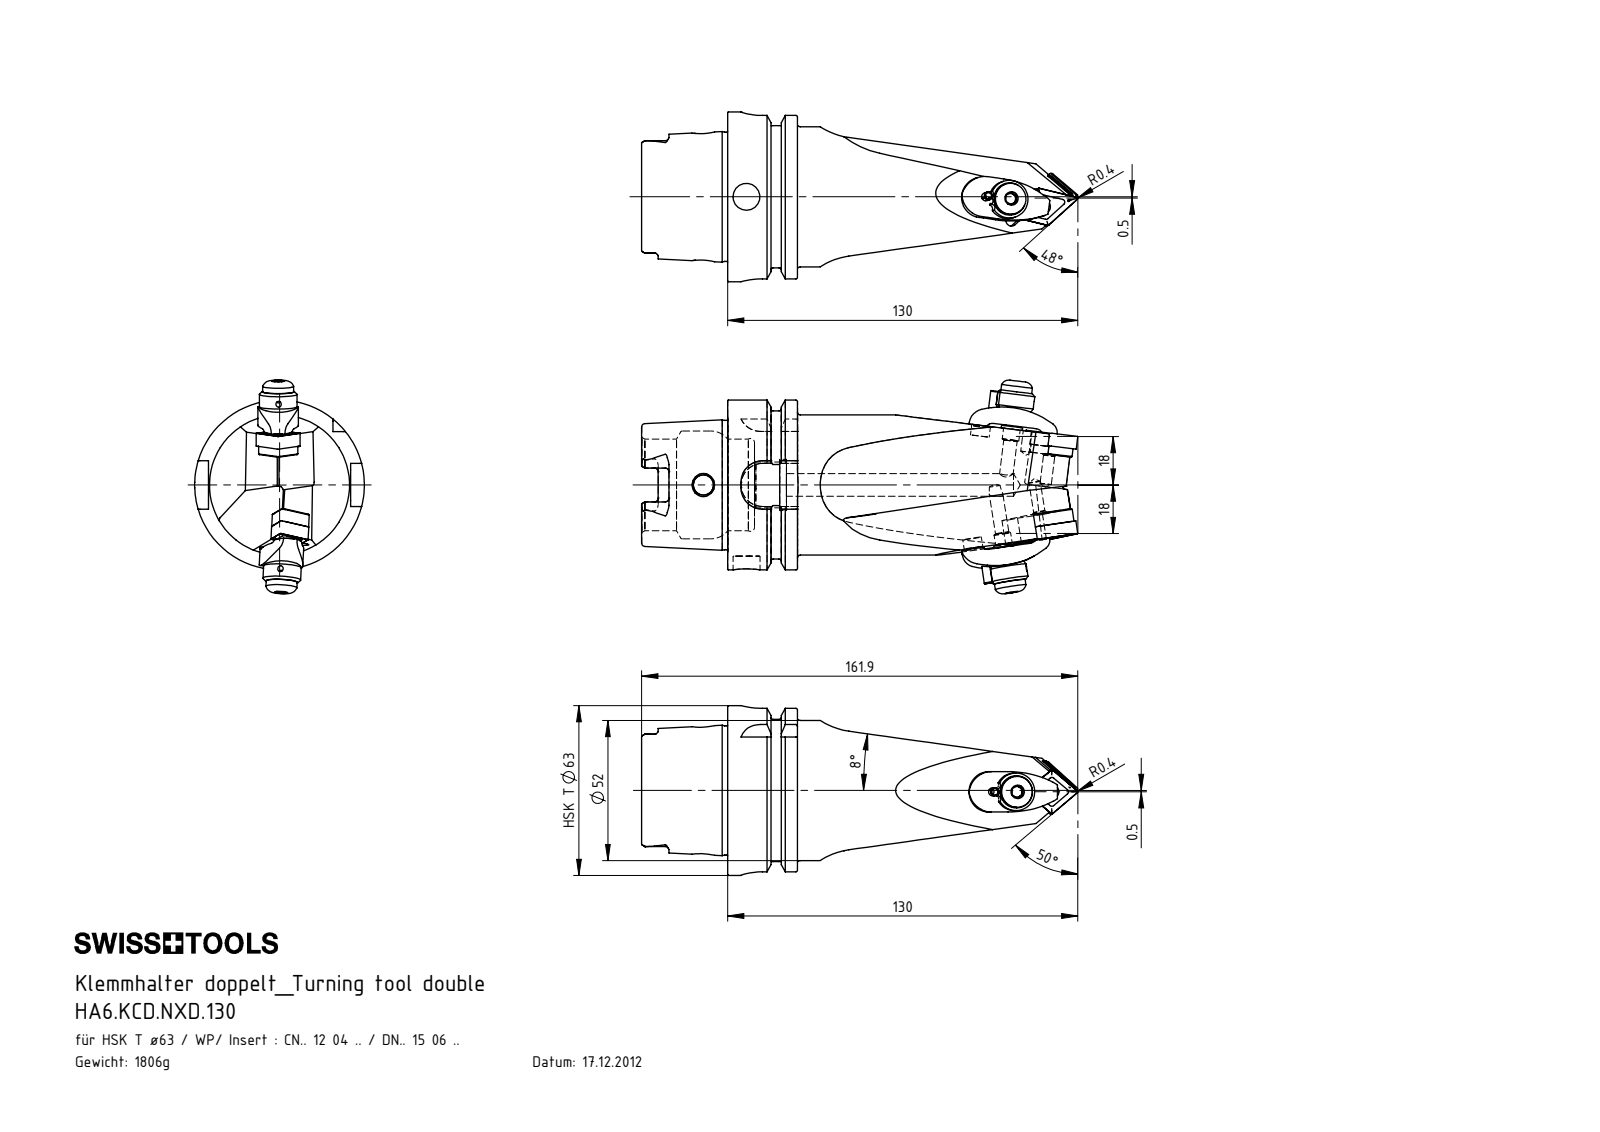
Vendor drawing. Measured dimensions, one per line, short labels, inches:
name: WCD-ER2.101.003_A; DNMG150404; WCC-ER5.102.012_B; WDF-ER2.101.004_A (+8 more)
written by: SolidWorks 2017 (AUTOMOTIVE_DESIGN)
unit: in
bodies: 17 solids, 517 faces (197 planar, 160 cylindrical, 160 other)
size: 6.374 × 3.123 × 2.48
volume: 13.94 in³; area: 75.7 in²
holes: 6× ⌀0.079, 4× ⌀0.276, 3× ⌀0.165, 2× ⌀0.094, 2× ⌀0.118, 2× ⌀0.197, 2× ⌀0.203, 2× ⌀0.244, 2× ⌀0.252, 2× ⌀0.335, 1× ⌀0.295, 1× ⌀0.331
bosses: 4× ⌀0.118, 2× ⌀0.551, 2× ⌀0.453, 2× ⌀0.276, 2× ⌀0.268, 2× ⌀0.244, 2× ⌀0.236, 2× ⌀0.197
rounds: 12× R0.015, 8× R0.016, 8× R0.039, 6× R0.027, 6× R0.027, 6× R0.055, 6× R0.059, 4× R0.079
face distances: 0.63, 1.022, 0.392, 0.187, 0.694, 0.227, 1.256, 1.648, 2.278, 2.079
hole spacings: 0.315, 0.591, 0.906, 0.323, 0.59, 0.905, 0.315, 0.315
